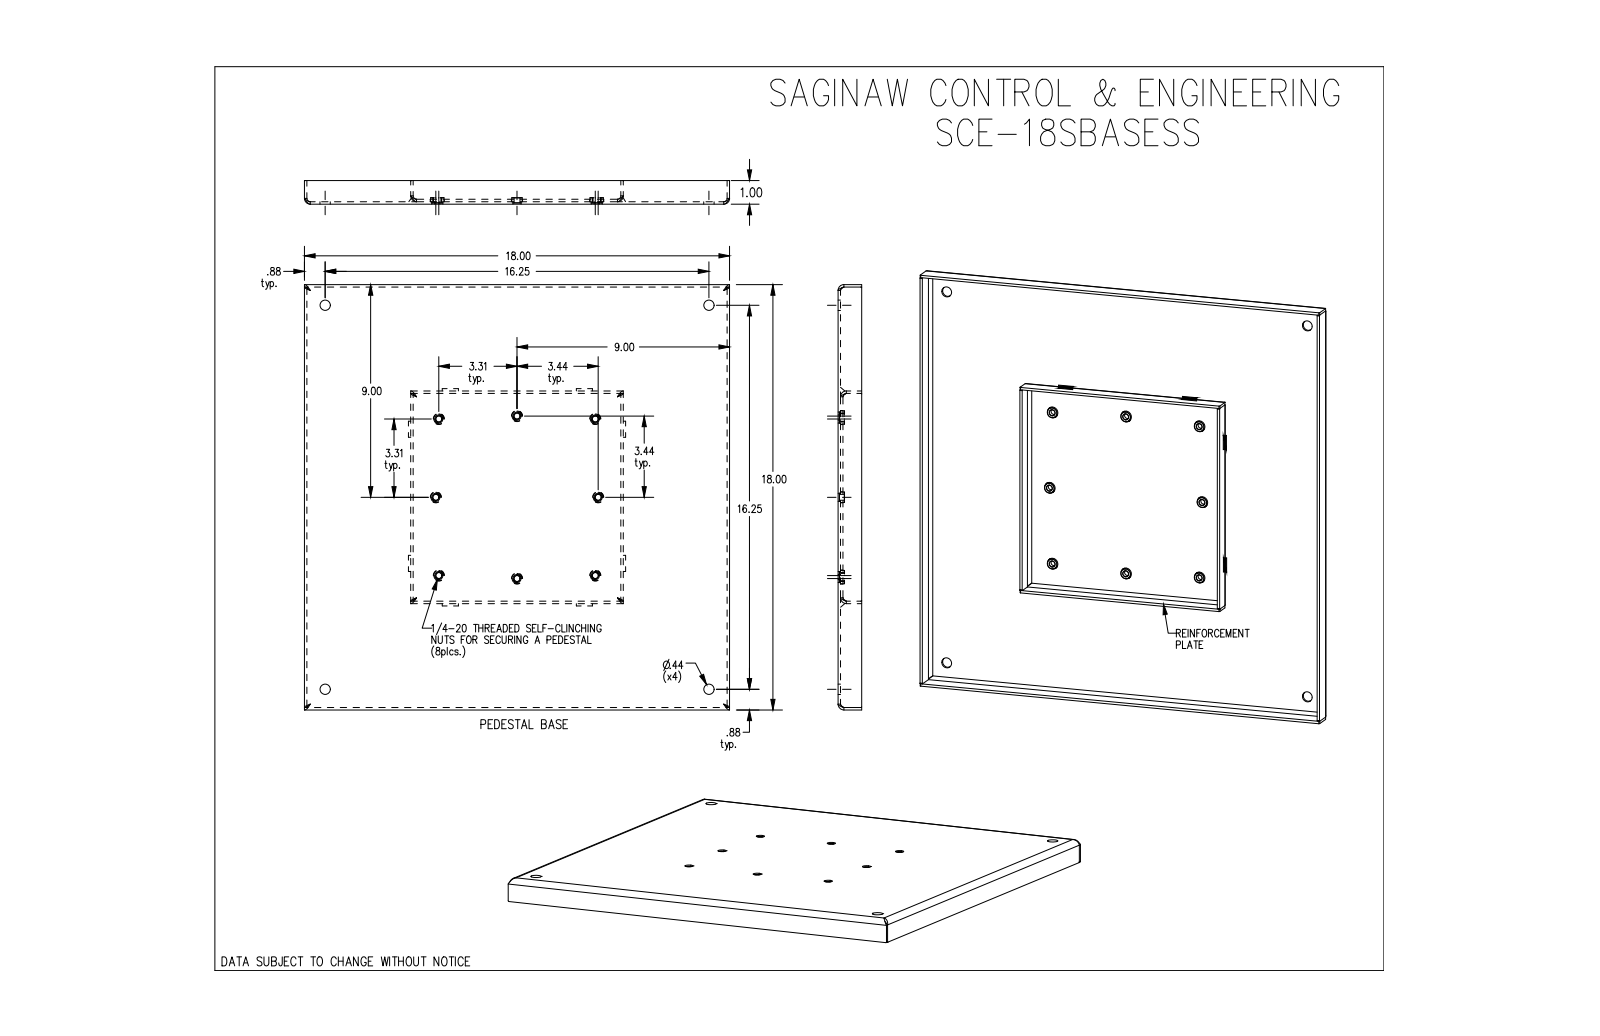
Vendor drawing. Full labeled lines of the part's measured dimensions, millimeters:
Part name (STEP PRODUCT): SCE-18SBASE
STEP written by: SolidWorks 2021 (AUTOMOTIVE_DESIGN)
Units: millimetres
Bodies: 9 solids, 151 faces (35 planar, 68 cylindrical, 48 other)
Overall size (bounding box): 457.2 × 457.2 × 25.4
Volume: 1 156 000 mm³ · Surface area: 496 400 mm²
Round holes (diameter × count): ⌀6.4 ×8, ⌀6.9 ×7, ⌀11.1 ×4
Round bosses / shafts (diameter × count): ⌀11.2 ×8, ⌀8.7 ×8
Partial cylindrical surfaces — rounded edges, fillets, slot ends (radius × count): R3.3 ×4, R8.1 ×4
Main face-to-face distances: 4.8, 452.4, 457.2, 447.6, 20.6, 25.4, 16.3, 4.3, 9.1, 22.8
Hole centre spacings: 84.2, 191, 315.2, 359, 123.5, 168.3, 172.9, 238.3
